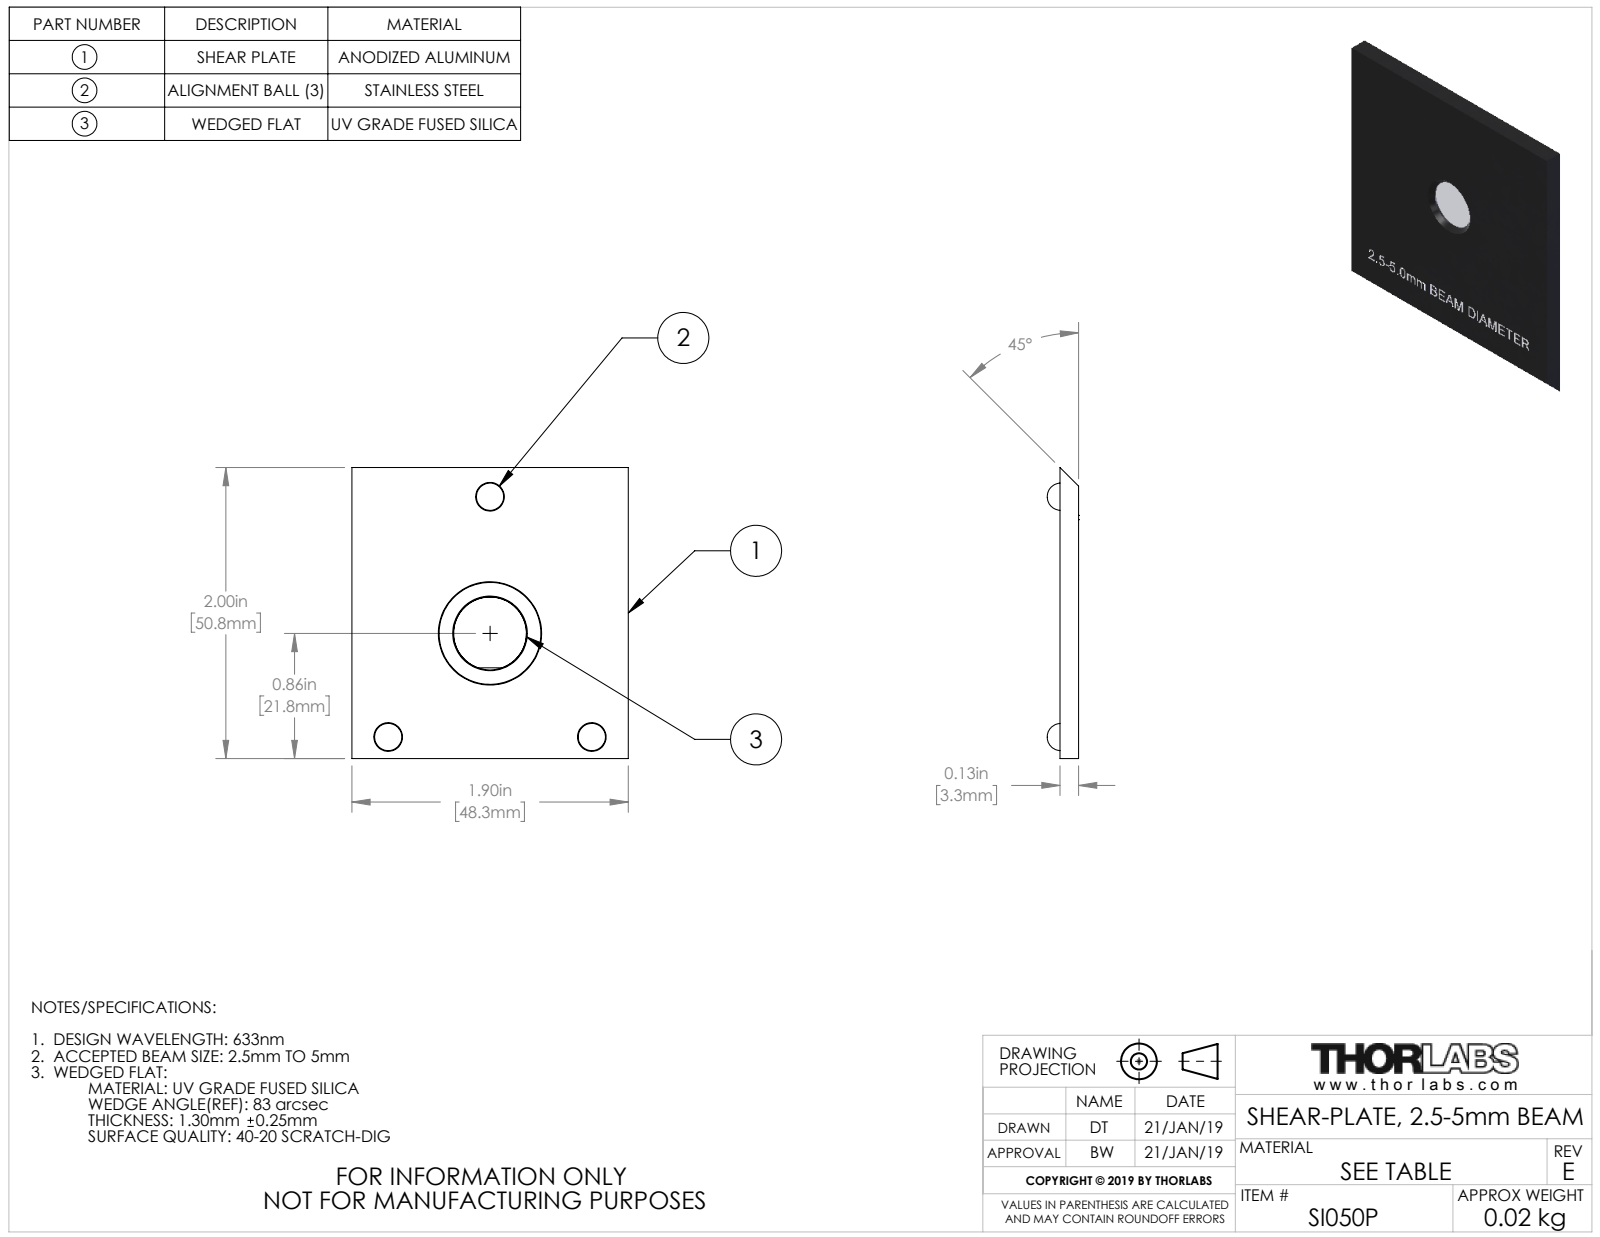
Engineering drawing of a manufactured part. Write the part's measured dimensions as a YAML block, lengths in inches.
part_name: "16655-E0W"
step_written_by: "SolidWorks 2018 (CONFIG_CONTROL_DESIGN)"
units: inches
bodies: {solids: 5, faces: 336, planar: 216, cylindrical: 13, other: 107}
overall_size: [2, 1.9, 0.216]
volume: 0.452
surface_area: 9.412
round_holes:
  - {diameter: 0.187, count: 3}
  - {diameter: 0.346, count: 1}
  - {diameter: 0.502, count: 1}
  - {diameter: 0.7, count: 1}
round_bosses_or_shafts:
  - {diameter: 0.5, count: 1}
face_to_face_distances: [0.128, 0.048, 0.08, 1.9, 0.051, 0.099, 0.029, 0.026, 0.025, 0.073]
hole_center_spacings: [0.998, 1.793, 0.939, 1.4]
